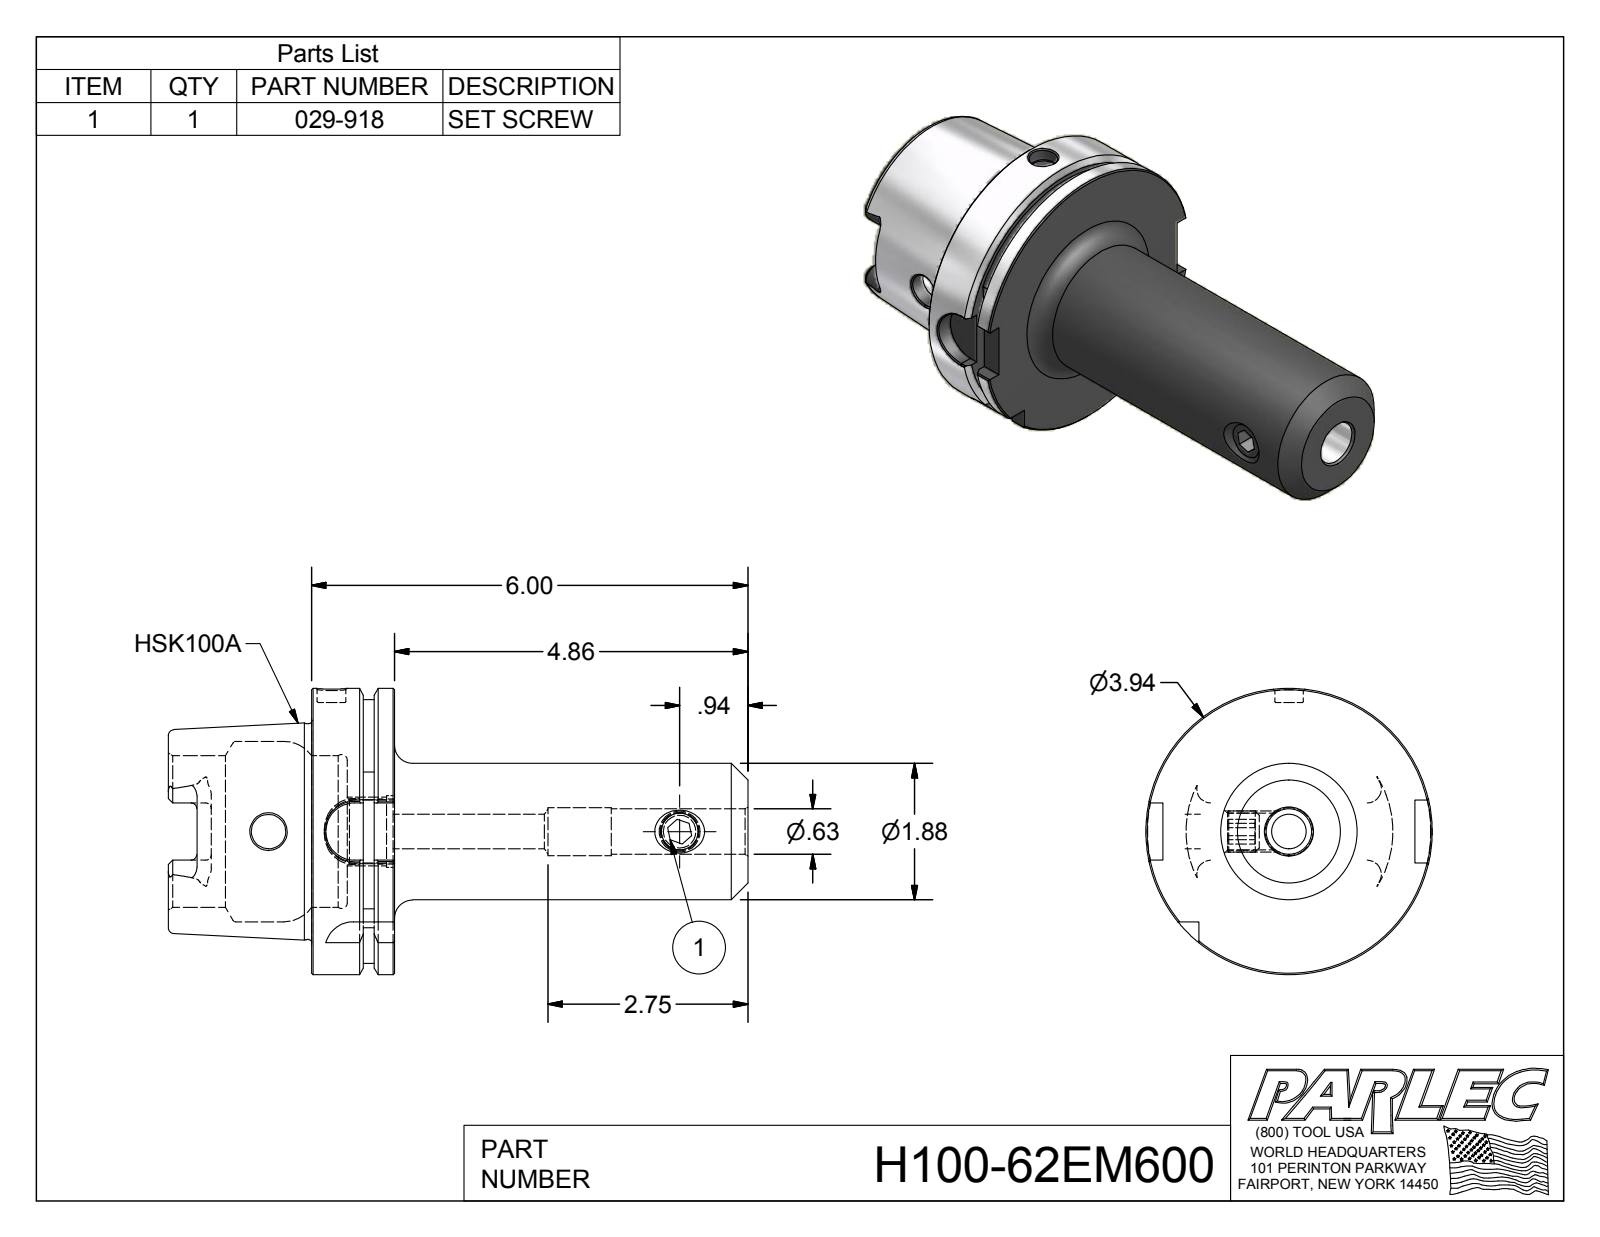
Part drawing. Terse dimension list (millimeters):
name: H100-62EM600; 029-918
written by: Autodesk Inventor 2012 (AUTOMOTIVE_DESIGN)
unit: mm
bodies: 2 solids, 140 faces (53 planar, 36 cylindrical, 51 other)
size: 202.4 × 100 × 100
volume: 451 300 mm³; area: 74 320 mm²
holes: 2× ⌀12, 1× ⌀10, 1× ⌀12.8, 1× ⌀15.9, 1× ⌀16.8, 1× ⌀22.4, 1× ⌀25, 1× ⌀53, 1× ⌀63
bosses: 1× ⌀100, 1× ⌀75.4, 1× ⌀47.6, 1× ⌀14.3
rounds: 6× R2, 4× R4.9, 4× R10, 1× R46
face distances: 29, 12.5, 16.5, 50, 62.5, 79, 202.4, 152.4, 139.9, 123.4
hole spacings: 143.6
